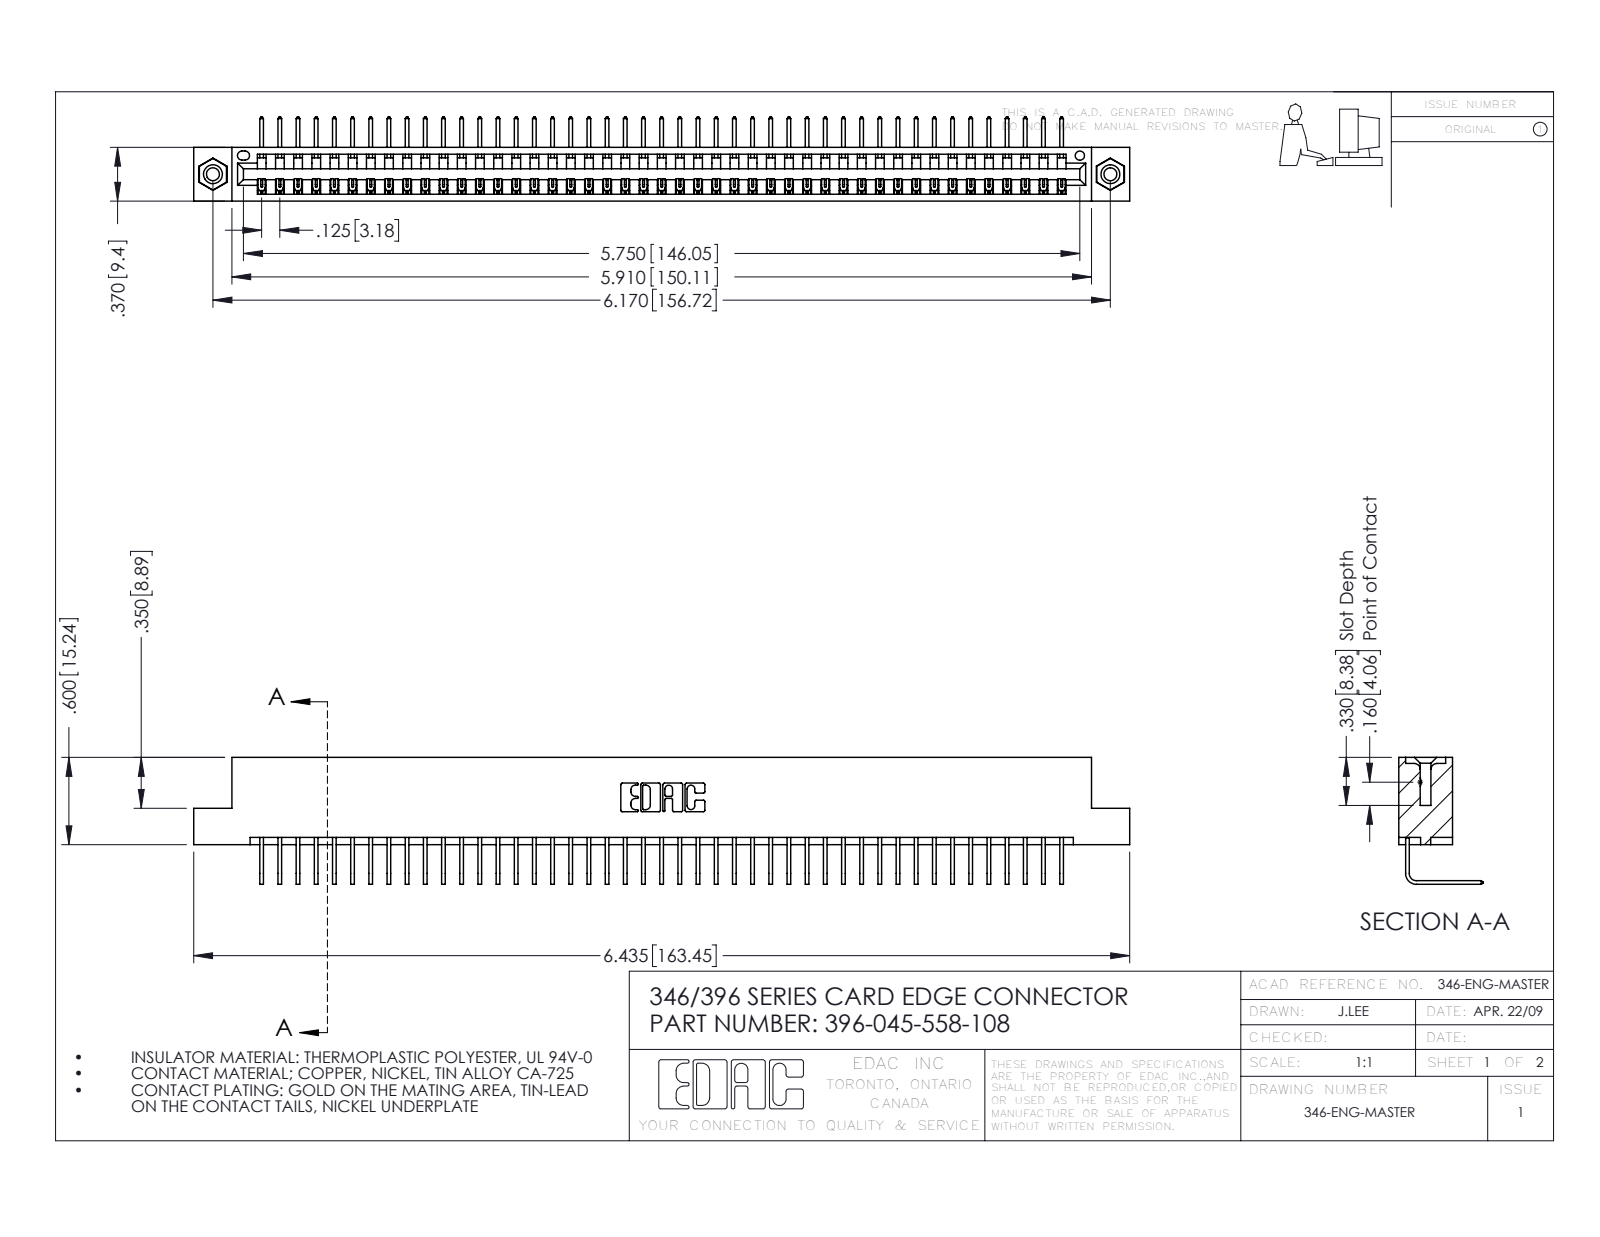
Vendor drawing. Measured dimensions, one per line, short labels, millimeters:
name: 345-250-001_345-250-003-102; 396-045-558-108; 346 Part_Flush Mounting Lugs - 0.156 Dia-TI; 345-292-001_558 Tail - 2
written by: SolidWorks 2016 (CONFIG_CONTROL_DESIGN)
unit: mm
bodies: 48 solids, 2882 faces (1998 planar, 868 cylindrical, 16 other)
size: 163.4 × 22.2 × 14.7
volume: 15 800 mm³; area: 20 710 mm²
holes: 2× ⌀2.3, 2× ⌀3.2, 2× ⌀4, 1× ⌀1.6
bosses: 2× ⌀3.9
rounds: 90× R0.2, 22× R0.3, 6× R0.2, 6× R0.8, 3× R0.7, 2× R0.8, 2× R1, 1× R0.4
face distances: 8.2, 1.2, 9.4, 6.4, 7.6, 0.6, 1.8, 3.8, 5.6, 2.5
hole spacings: 6.2, 151.4, 156.7
